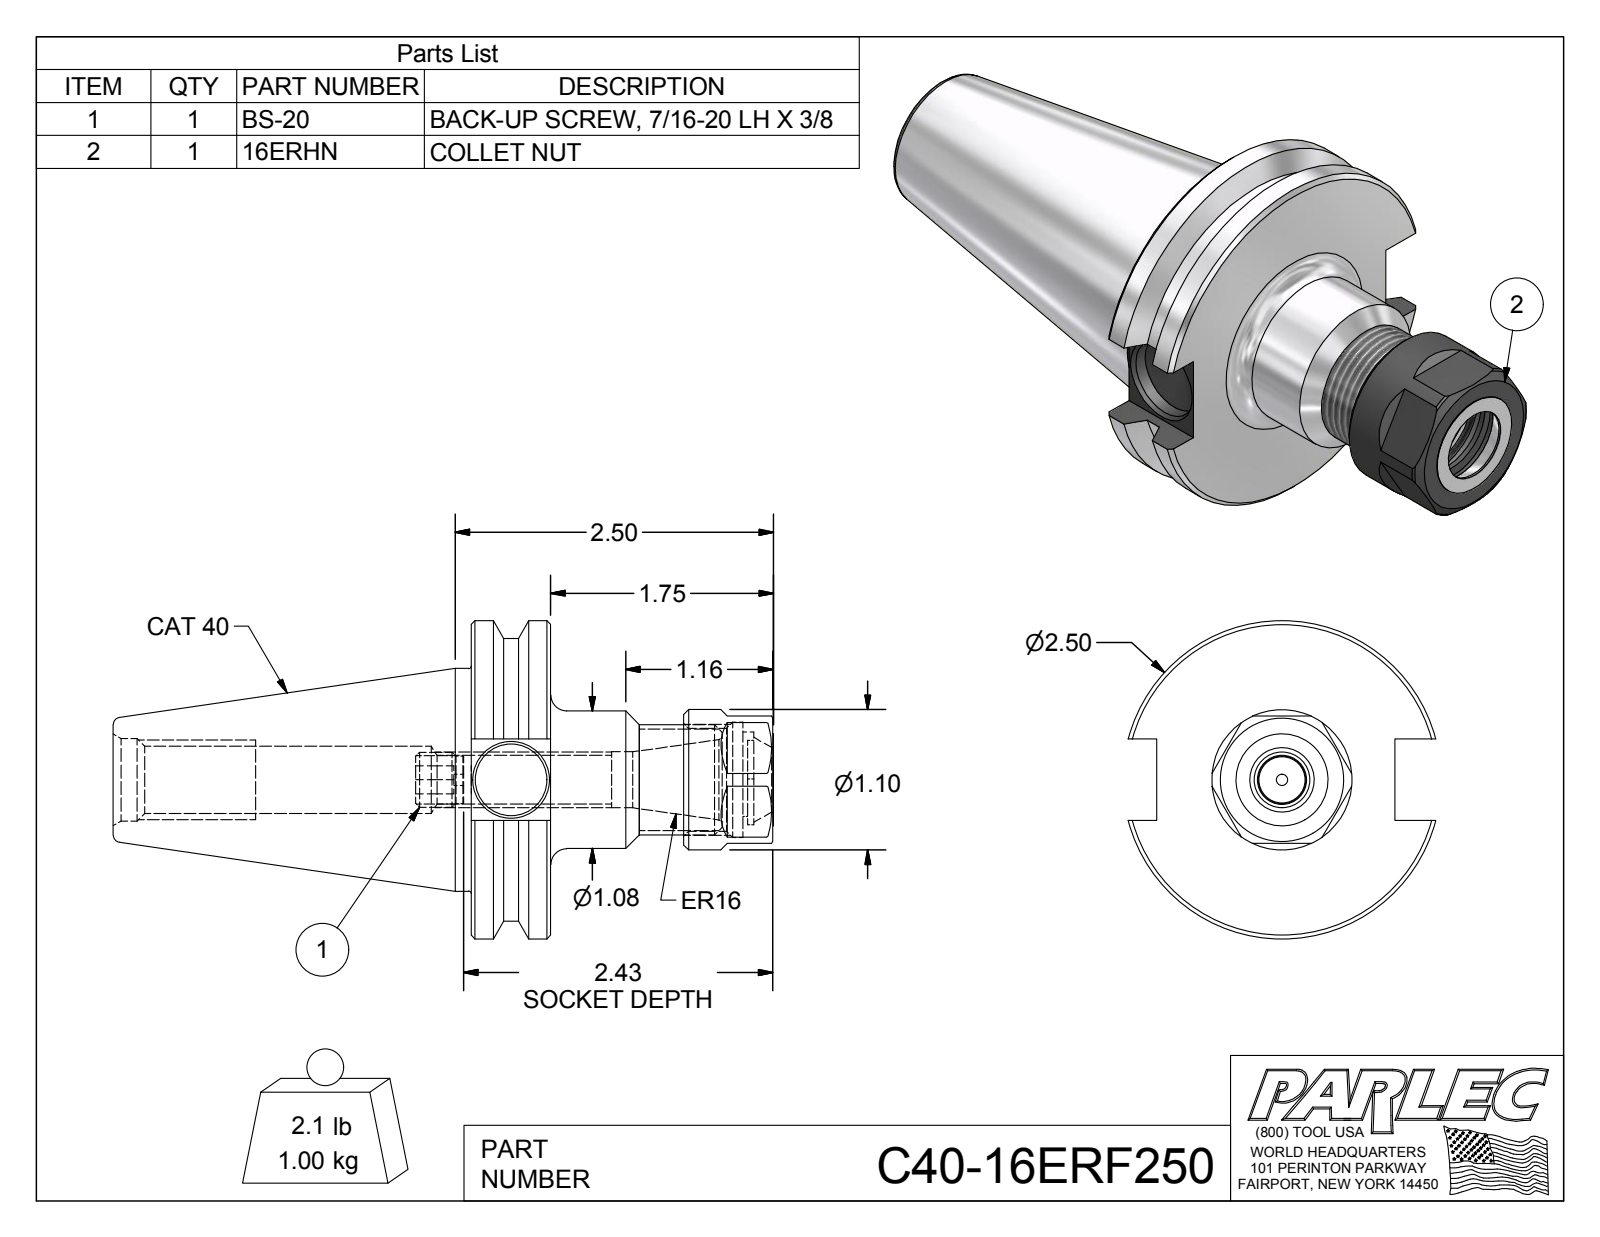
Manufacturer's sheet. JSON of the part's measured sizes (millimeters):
{"part_name": "C40-16ER2-1; BS-20; 16ERHN; C40-16ERF250", "step_written_by": "Autodesk Inventor 2016 (AUTOMOTIVE_DESIGN)", "units": "millimeters", "bodies": {"solids": 3, "faces": 98, "planar": 38, "cylindrical": 25, "other": 35}, "overall_size": [131.76, 63.5, 61.38], "volume_mm3": 120099, "surface_area_mm2": 27655, "round_holes": [[2.29, 1], [8, 1], [9.73, 1], [10.13, 1], [11.18, 1], [12.4, 1], [13.39, 1], [16.46, 1], [17.02, 1], [20.5, 1], [23, 1]], "round_bosses_or_shafts": [[63.5, 1], [56.36, 1], [44.45, 1], [28, 1], [27.43, 1], [22, 1], [10.97, 1], [9.46, 1]], "partial_cylinders_radius": [[7.24, 1], [9, 1]], "face_to_face_distances": [15.88, 60.33, 44.45, 25.14, 4.44, 20.7, 54.63, 38.75, 5.7, 16.26], "hole_center_spacings": [1.52]}
